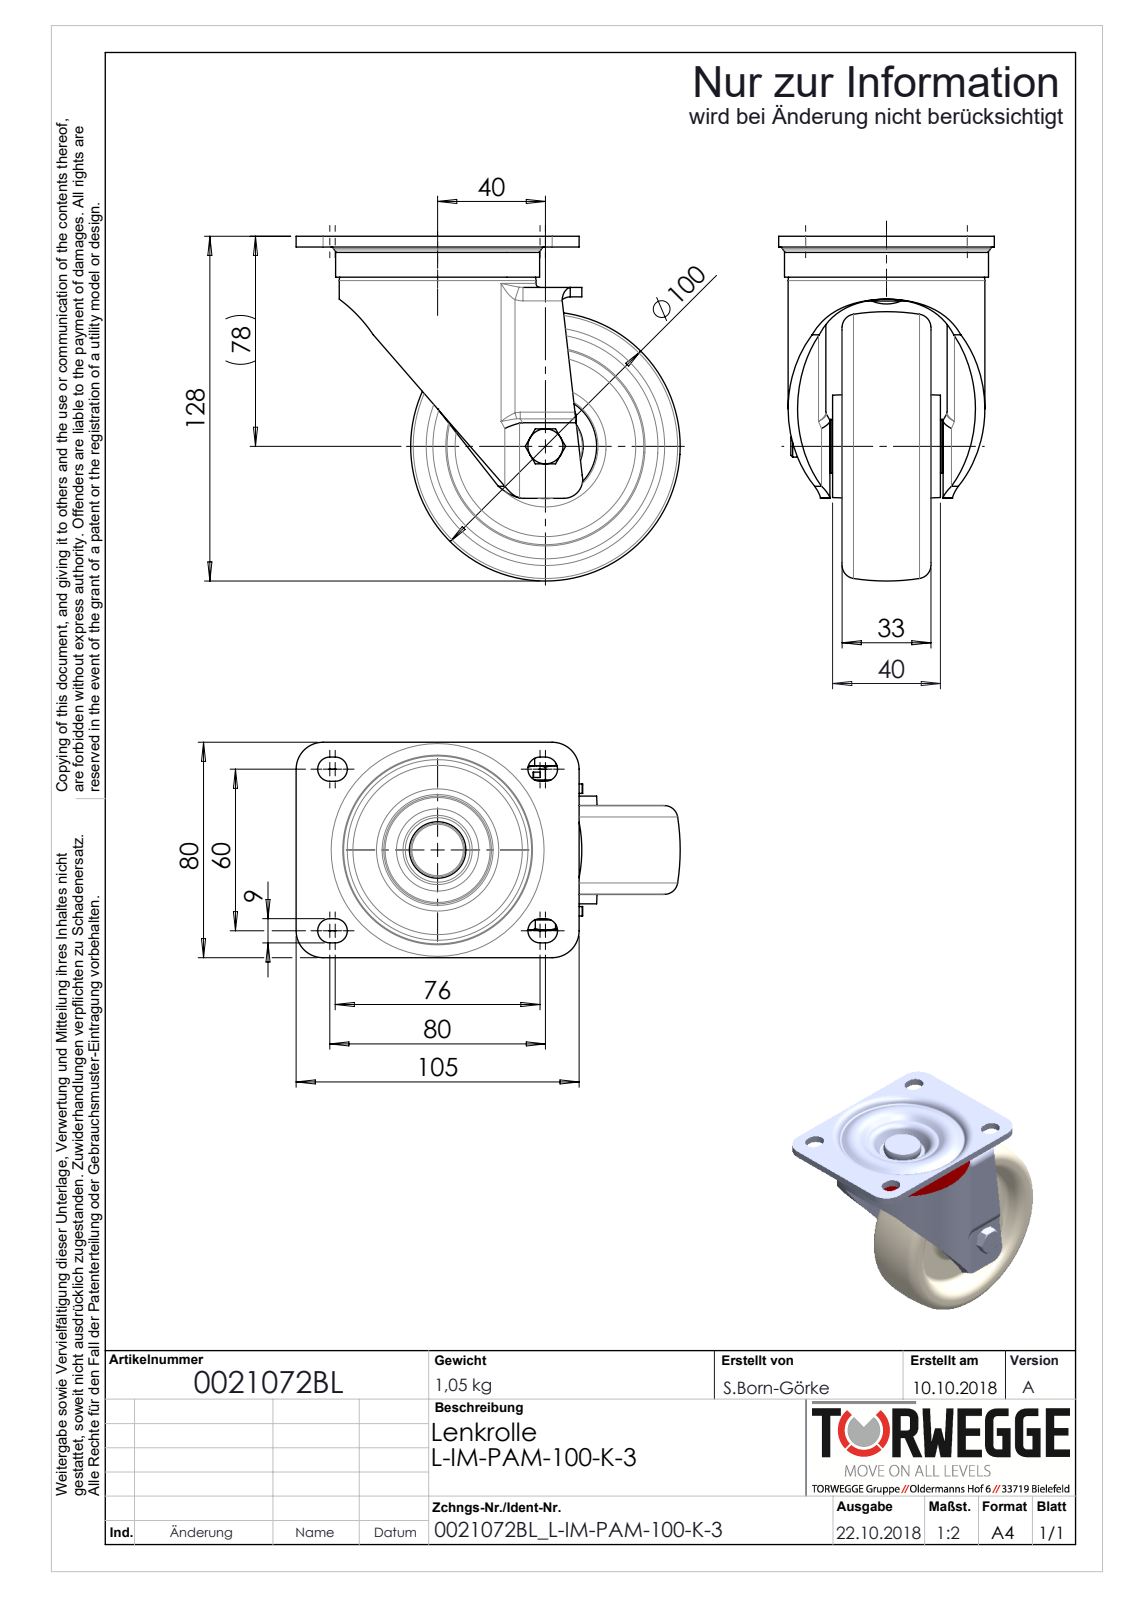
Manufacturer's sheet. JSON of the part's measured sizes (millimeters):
{"part_name": "0021072_L-IM-PAM-100-K-3", "step_written_by": "SolidWorks 2014 (AUTOMOTIVE_DESIGN)", "units": "millimeters", "bodies": {"solids": 19, "faces": 782, "planar": 343, "cylindrical": 192, "other": 247}, "overall_size": [142.5, 128, 80], "volume_mm3": 295465, "surface_area_mm2": 120690, "round_holes": [[6.8, 1], [8, 1], [8.2, 1], [8.5, 1], [12, 1], [12.5, 1], [16.8, 1], [23, 1], [23.2, 1], [35.1, 1], [35.5, 1], [46.75, 1]], "round_bosses_or_shafts": [[75.69, 1], [73, 1], [52.5, 1], [28, 1], [21, 1], [20, 1], [13, 1], [12.5, 1]], "partial_cylinders_radius": [[0.37, 8], [4.5, 8], [0.21, 7], [0.62, 7], [0.12, 4], [0.86, 4], [0.93, 4], [1.5, 4]], "face_to_face_distances": [4, 3.5, 1.5, 1, 47, 17.5, 15, 5, 2.5, 25]}
